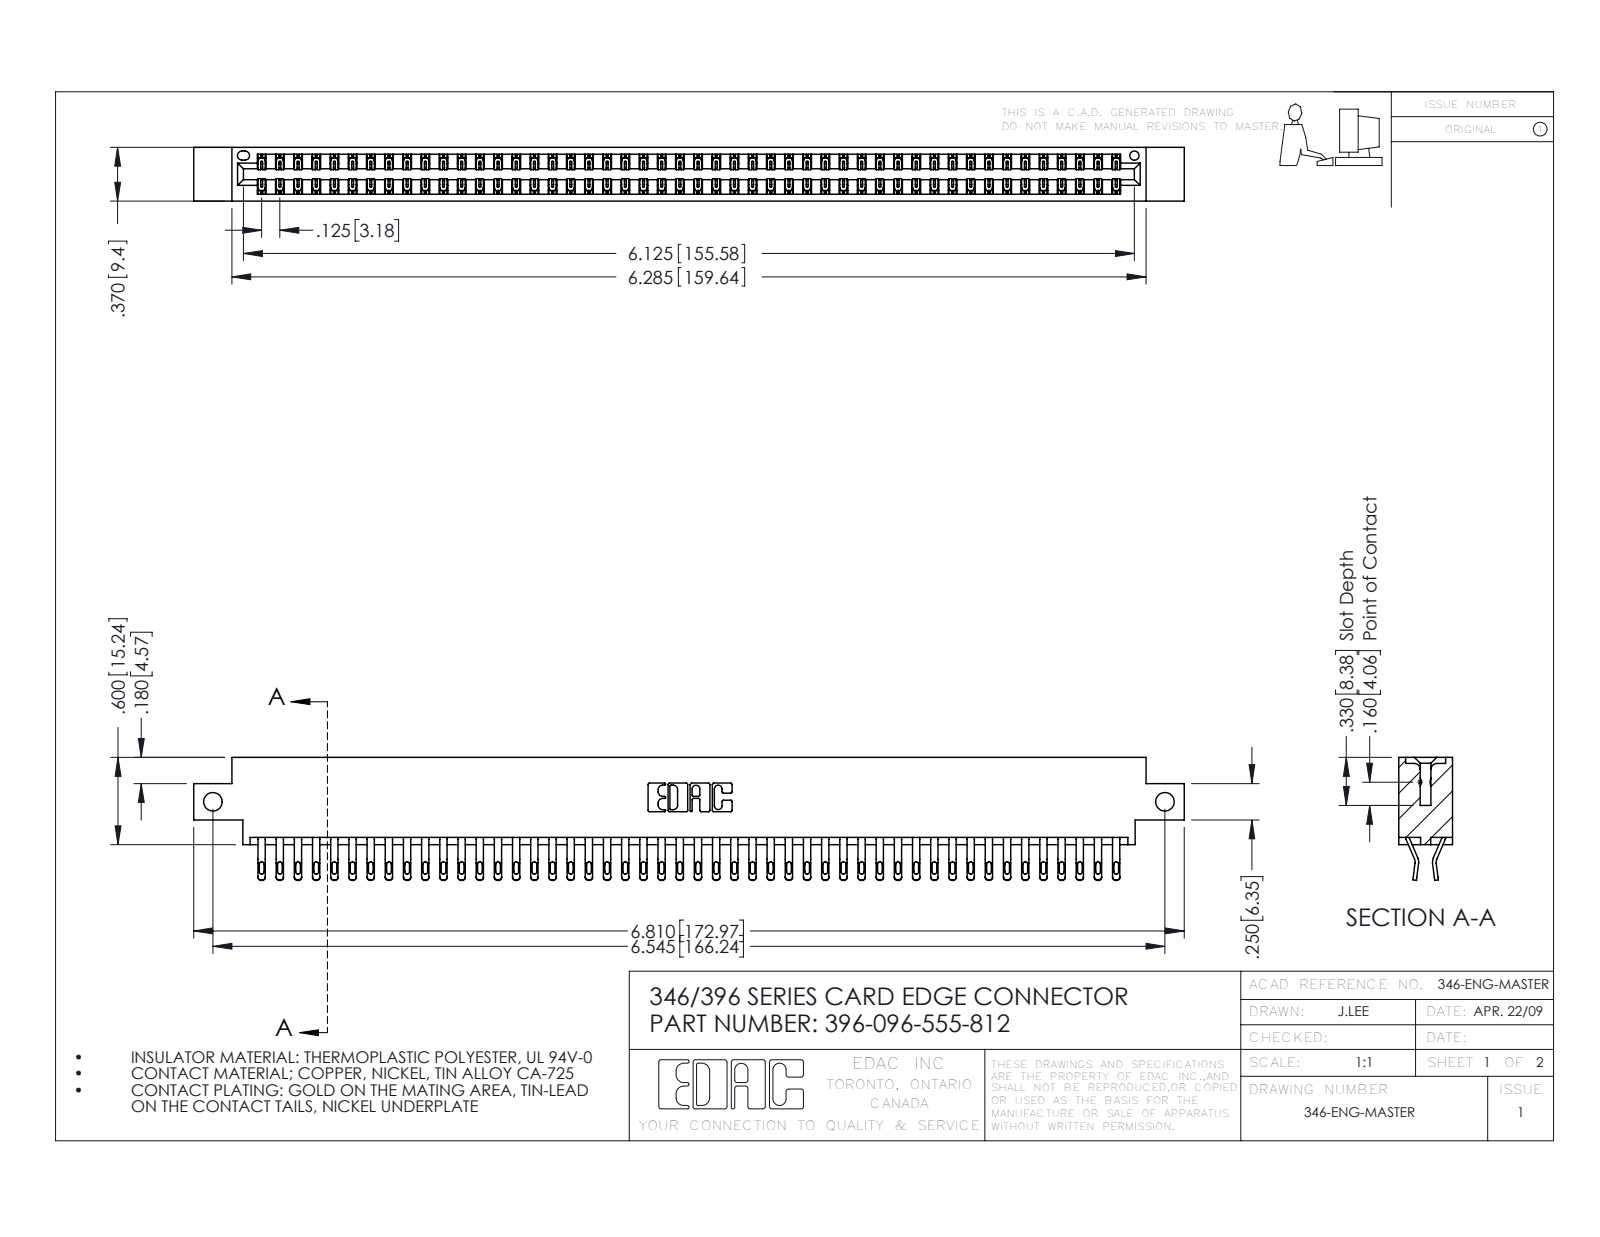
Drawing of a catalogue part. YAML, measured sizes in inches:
part_name: "345-292-001_555 Tail; 396-096-555-812; 346 Part_0.170 Offset - Side Mount"
step_written_by: "SolidWorks 2016 (CONFIG_CONTROL_DESIGN)"
units: inches
bodies: {solids: 97, faces: 5694, planar: 3248, cylindrical: 2446, other: 0}
overall_size: [6.81, 0.845, 0.37]
volume: 1.034
surface_area: 37.86
round_holes:
  - {diameter: 0.128, count: 2}
  - {diameter: 0.064, count: 1}
partial_cylinders:
  - {radius: 0.016, count: 192}
  - {radius: 0.02, count: 192}
  - {radius: 0.006, count: 144}
  - {radius: 0.01, count: 22}
  - {radius: 0.007, count: 6}
  - {radius: 0.031, count: 6}
  - {radius: 0.026, count: 3}
  - {radius: 0.01, count: 2}
face_to_face_distances: [0.048, 0.322, 0.37, 0.25, 0.025, 0.072, 0.298, 0.275, 0.148, 0.222]
hole_center_spacings: [6.545]
